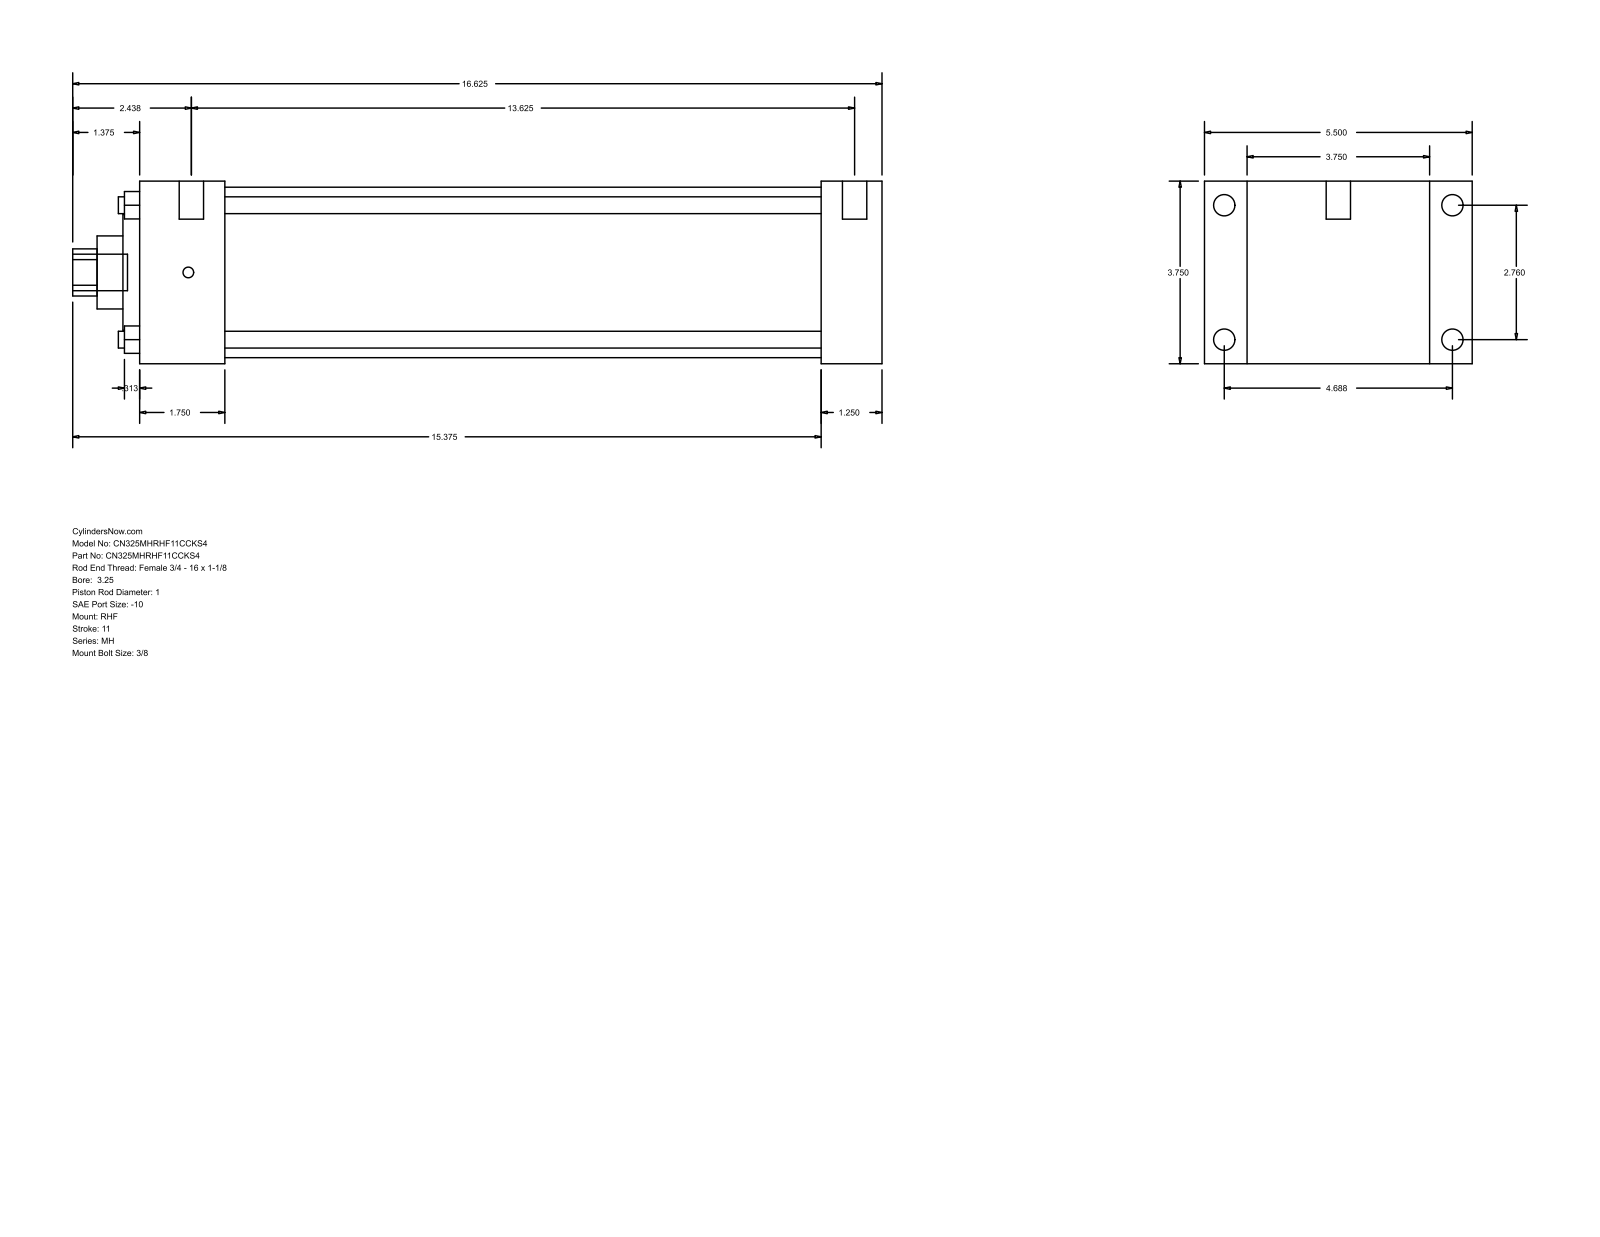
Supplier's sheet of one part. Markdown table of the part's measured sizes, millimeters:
| quantity | value |
| --- | --- |
| part name | MH_RHF__0325_1 |
| STEP written by | GSSL Pune (CONFIG_CONTROL_DESIGN) |
| units | millimeters |
| bodies | 0 solids, 90 faces (61 planar, 29 cylindrical, 0 other) |
| overall size | 422.27 × 139.7 × 95.25 |
| round holes (diameter × count) | 8.76 × 4, 25.4 × 1, 38.1 × 1, 60.33 × 1, 88.9 × 1 |
| round bosses / shafts (diameter × count) | 11.13 × 4, 5.56 × 4, 12.7 × 2, 19.05 × 1 |
| partial cylindrical surfaces (radius × count) | 12.29 × 1 |
| main face-to-face distances | 95.24, 31.75, 22.23, 117.47, 355.6, 387.35, 139.7, 44.46, 311.14, 342.89 |
| hole center spacings | 49.57, 70.1, 99.14 |
